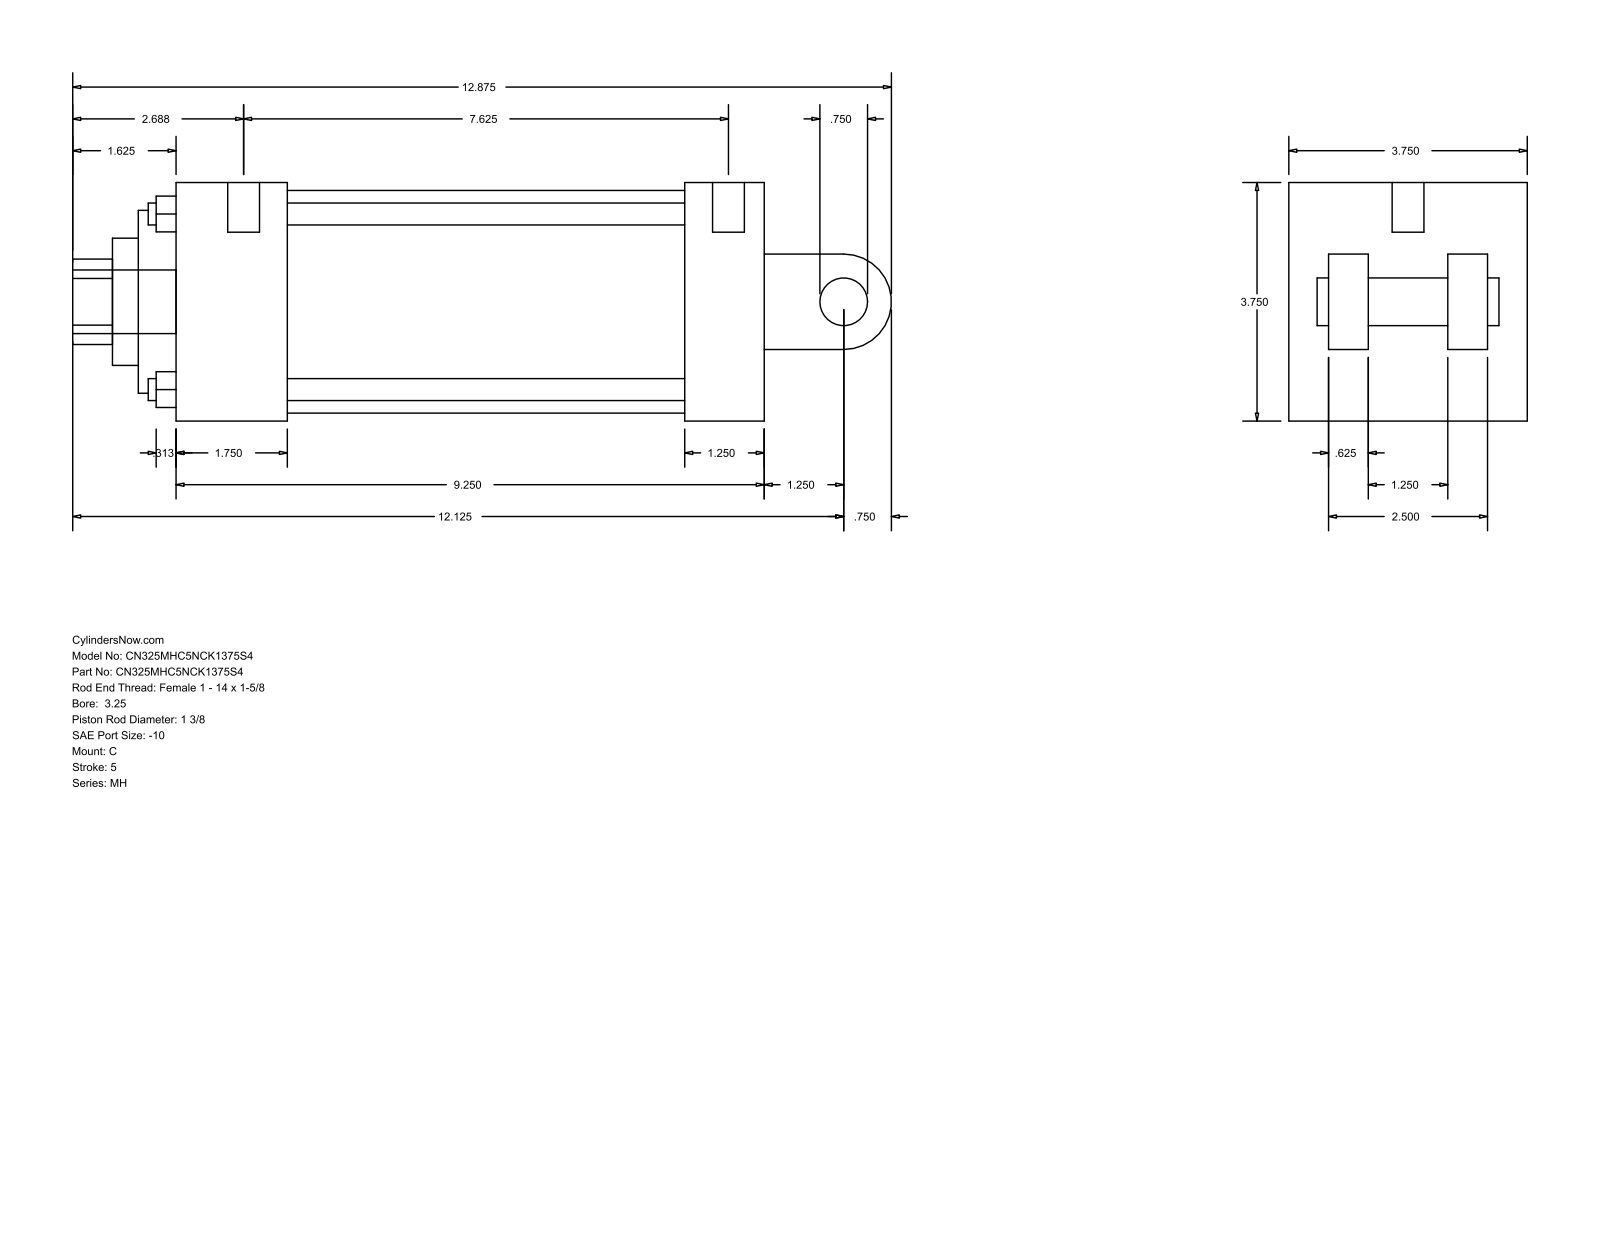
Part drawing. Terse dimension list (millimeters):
name: MH_C__0325_1.375
written by: GSSL Pune (CONFIG_CONTROL_DESIGN)
unit: mm
bodies: 0 solids, 101 faces (71 planar, 30 cylindrical, 0 other)
size: 327.02 × 95.25 × 95.25
holes: 4× ⌀8.76, 2× ⌀5.56, 1× ⌀12.7, 1× ⌀34.92, 1× ⌀50.8, 1× ⌀73.03, 1× ⌀88.9
bosses: 2× ⌀5.56, 1× ⌀25.4, 1× ⌀19.05, 1× ⌀12.7
rounds: 1× R17.06, 1× R19.05
face distances: 95.24, 15.87, 234.96, 63.5, 31.76, 79.37, 31.74, 47.63, 44.45, 203.2
hole spacings: 49.57, 70.1, 99.14, 4.76
